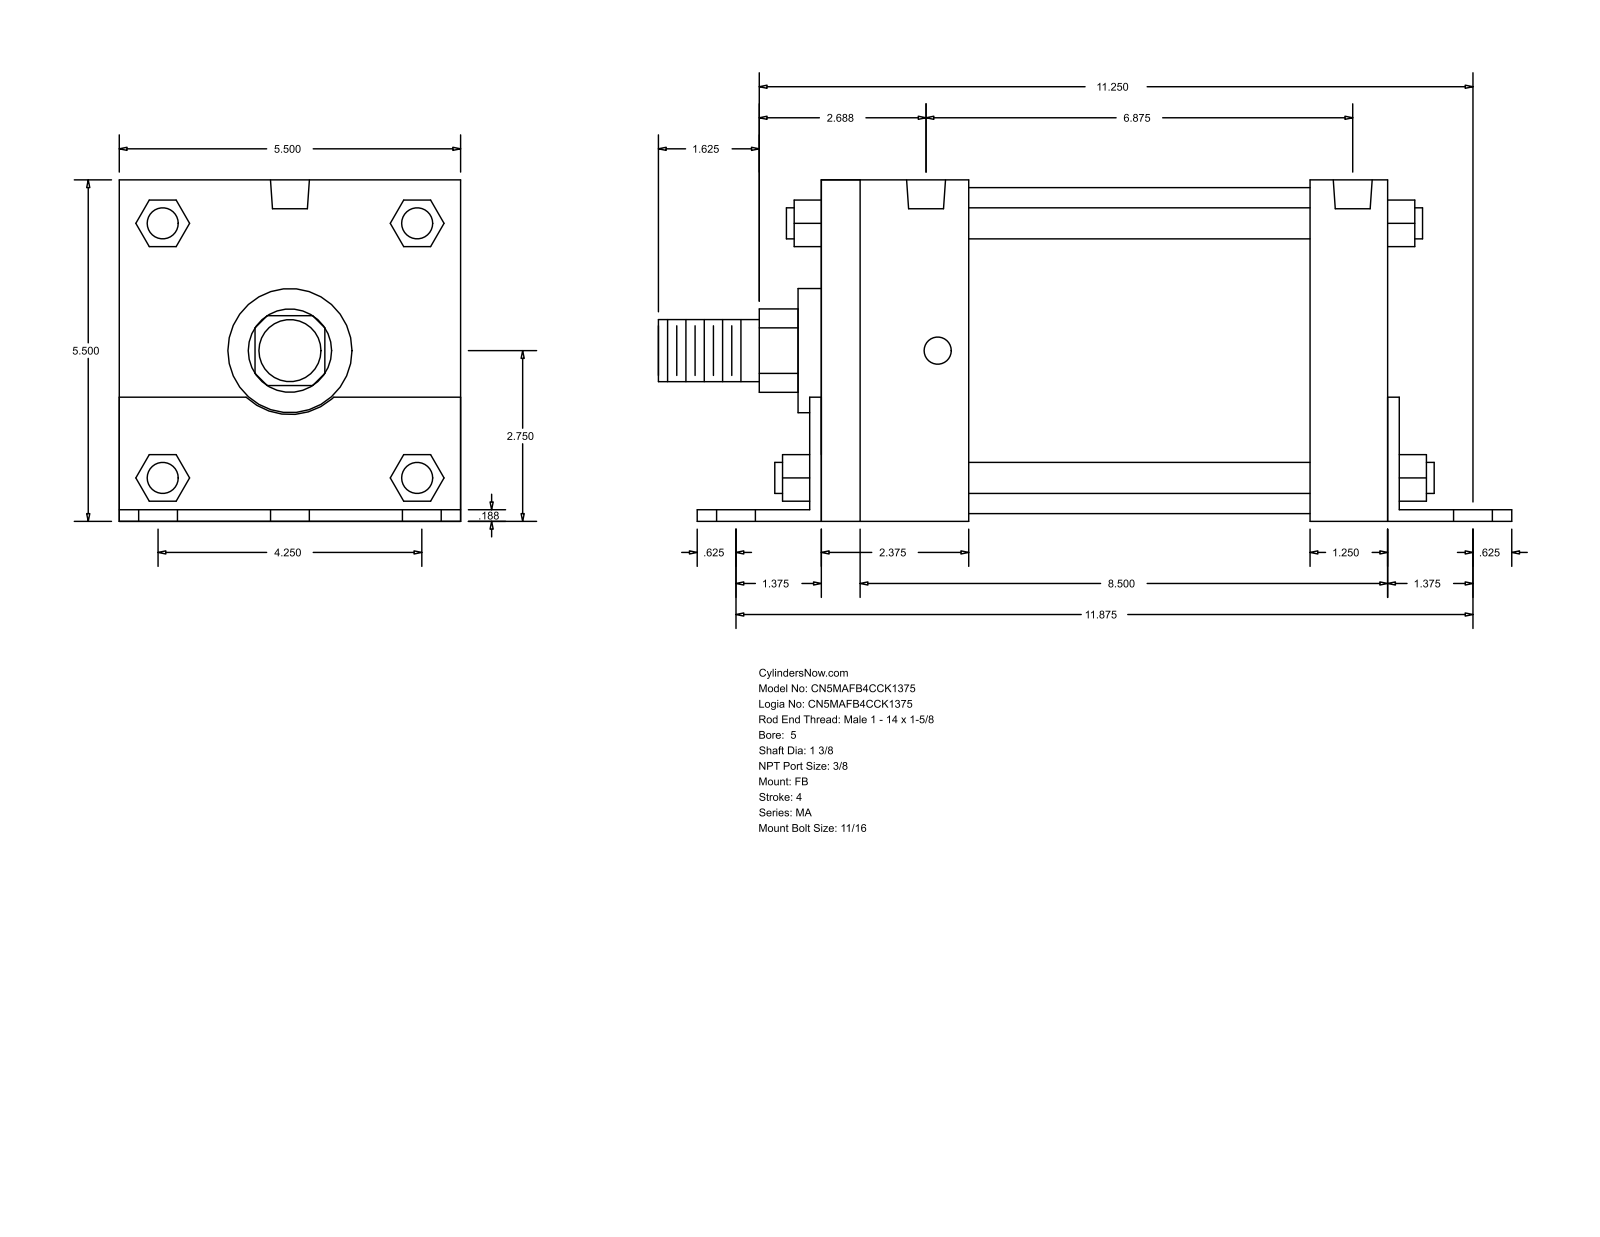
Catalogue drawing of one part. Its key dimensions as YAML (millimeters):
part_name: "MA_FB__0500_1.375"
step_written_by: "GSSL Pune (CONFIG_CONTROL_DESIGN)"
units: millimeters
bodies: {solids: 0, faces: 140, planar: 105, cylindrical: 35, other: 0}
overall_size: [349.25, 139.75, 139.7]
round_holes:
  - {diameter: 17.46, count: 6}
  - {diameter: 11.11, count: 4}
  - {diameter: 15.93, count: 2}
round_bosses_or_shafts:
  - {diameter: 12.7, count: 4}
  - {diameter: 133.35, count: 1}
  - {diameter: 50.8, count: 1}
  - {diameter: 34.92, count: 1}
  - {diameter: 25.4, count: 1}
partial_cylinders:
  - {radius: 17.06, count: 1}
  - {radius: 26.16, count: 1}
face_to_face_distances: [139.7, 4.76, 139.75, 236.54, 4.71, 134.99, 231.78, 241.3, 31.75, 36.51]
hole_center_spacings: [53.98, 306.42, 301.63, 4.77, 73.04, 76.34, 94.68, 98.64]
